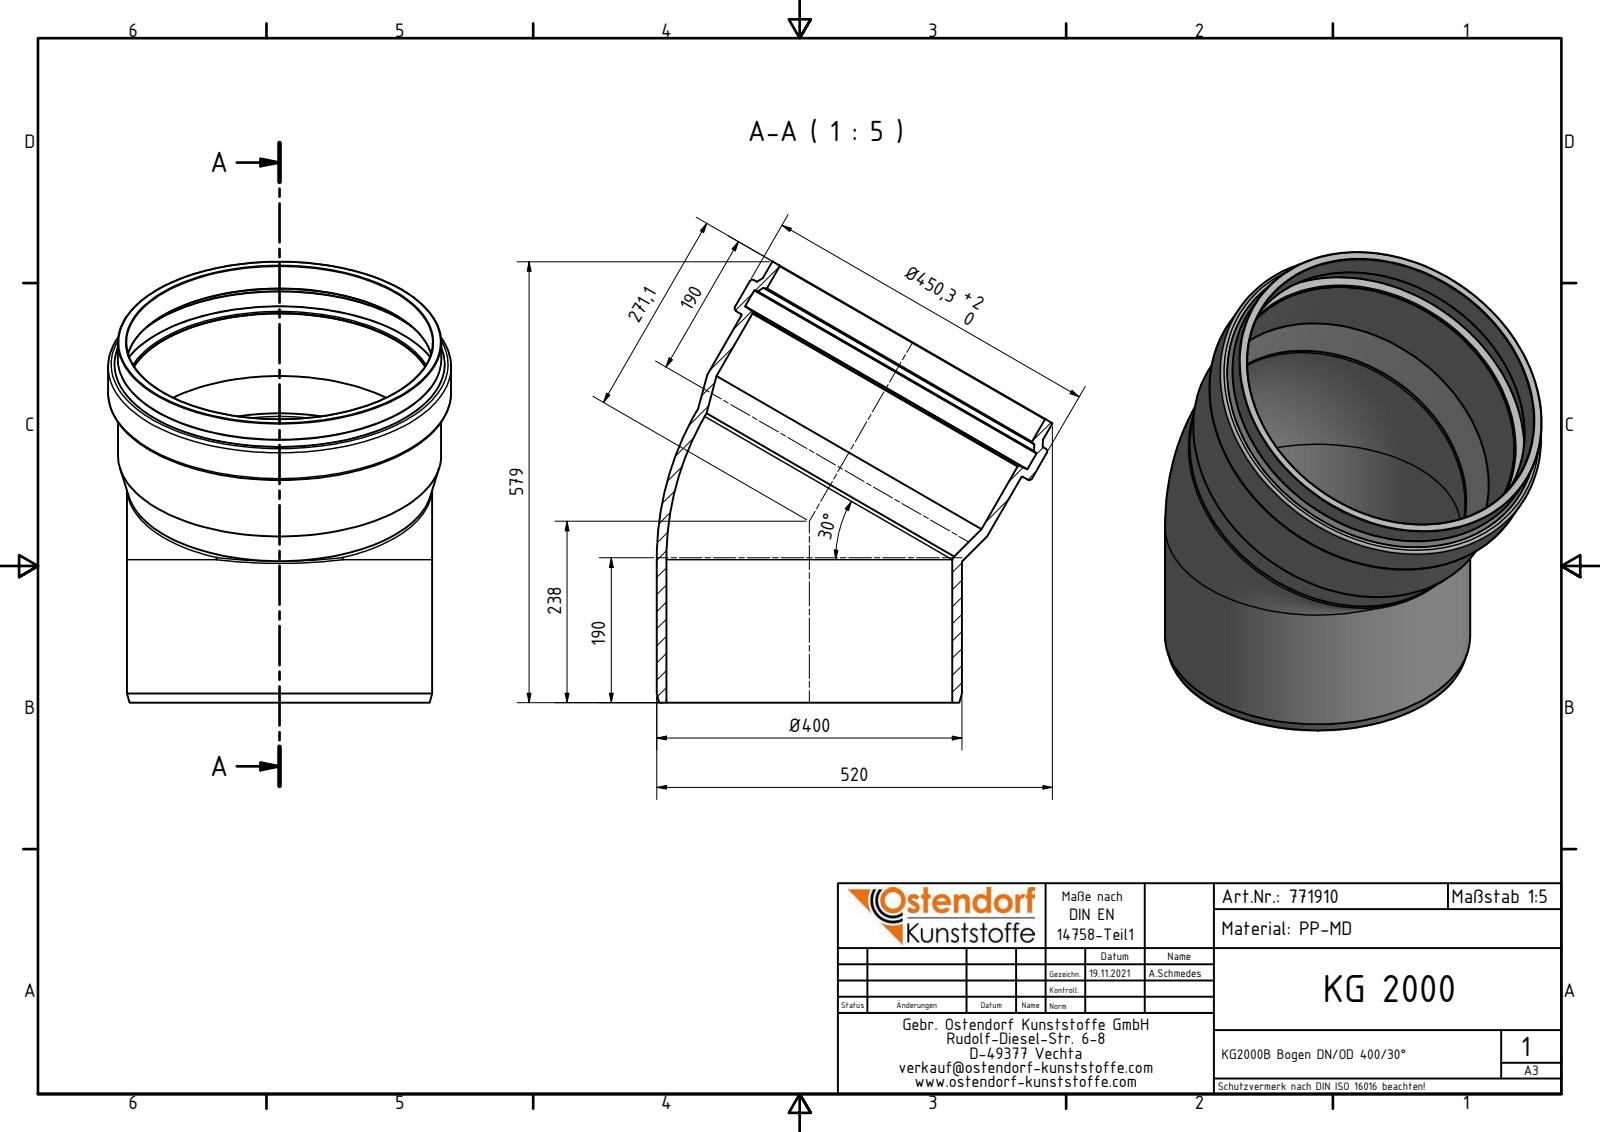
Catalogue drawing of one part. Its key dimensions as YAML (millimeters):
part_name: "771910 KG2000B Bogen DN_OD 400_30°"
step_written_by: "Autodesk Inventor 2020 (AUTOMOTIVE_DESIGN)"
units: millimeters
bodies: {solids: 1, faces: 40, planar: 5, cylindrical: 11, other: 24}
overall_size: [578.59, 519.33, 450.3]
volume: 7836000
surface_area: 1352000
round_holes:
  - {diameter: 375.5, count: 2}
  - {diameter: 401.7, count: 1}
  - {diameter: 402.1, count: 1}
  - {diameter: 427.7, count: 1}
round_bosses_or_shafts:
  - {diameter: 400.5, count: 2}
  - {diameter: 450.3, count: 1}
  - {diameter: 424.7, count: 1}
  - {diameter: 424.3, count: 1}
face_to_face_distances: [80.39, 47, 33.39, 8.13, 38.87, 72.26]
